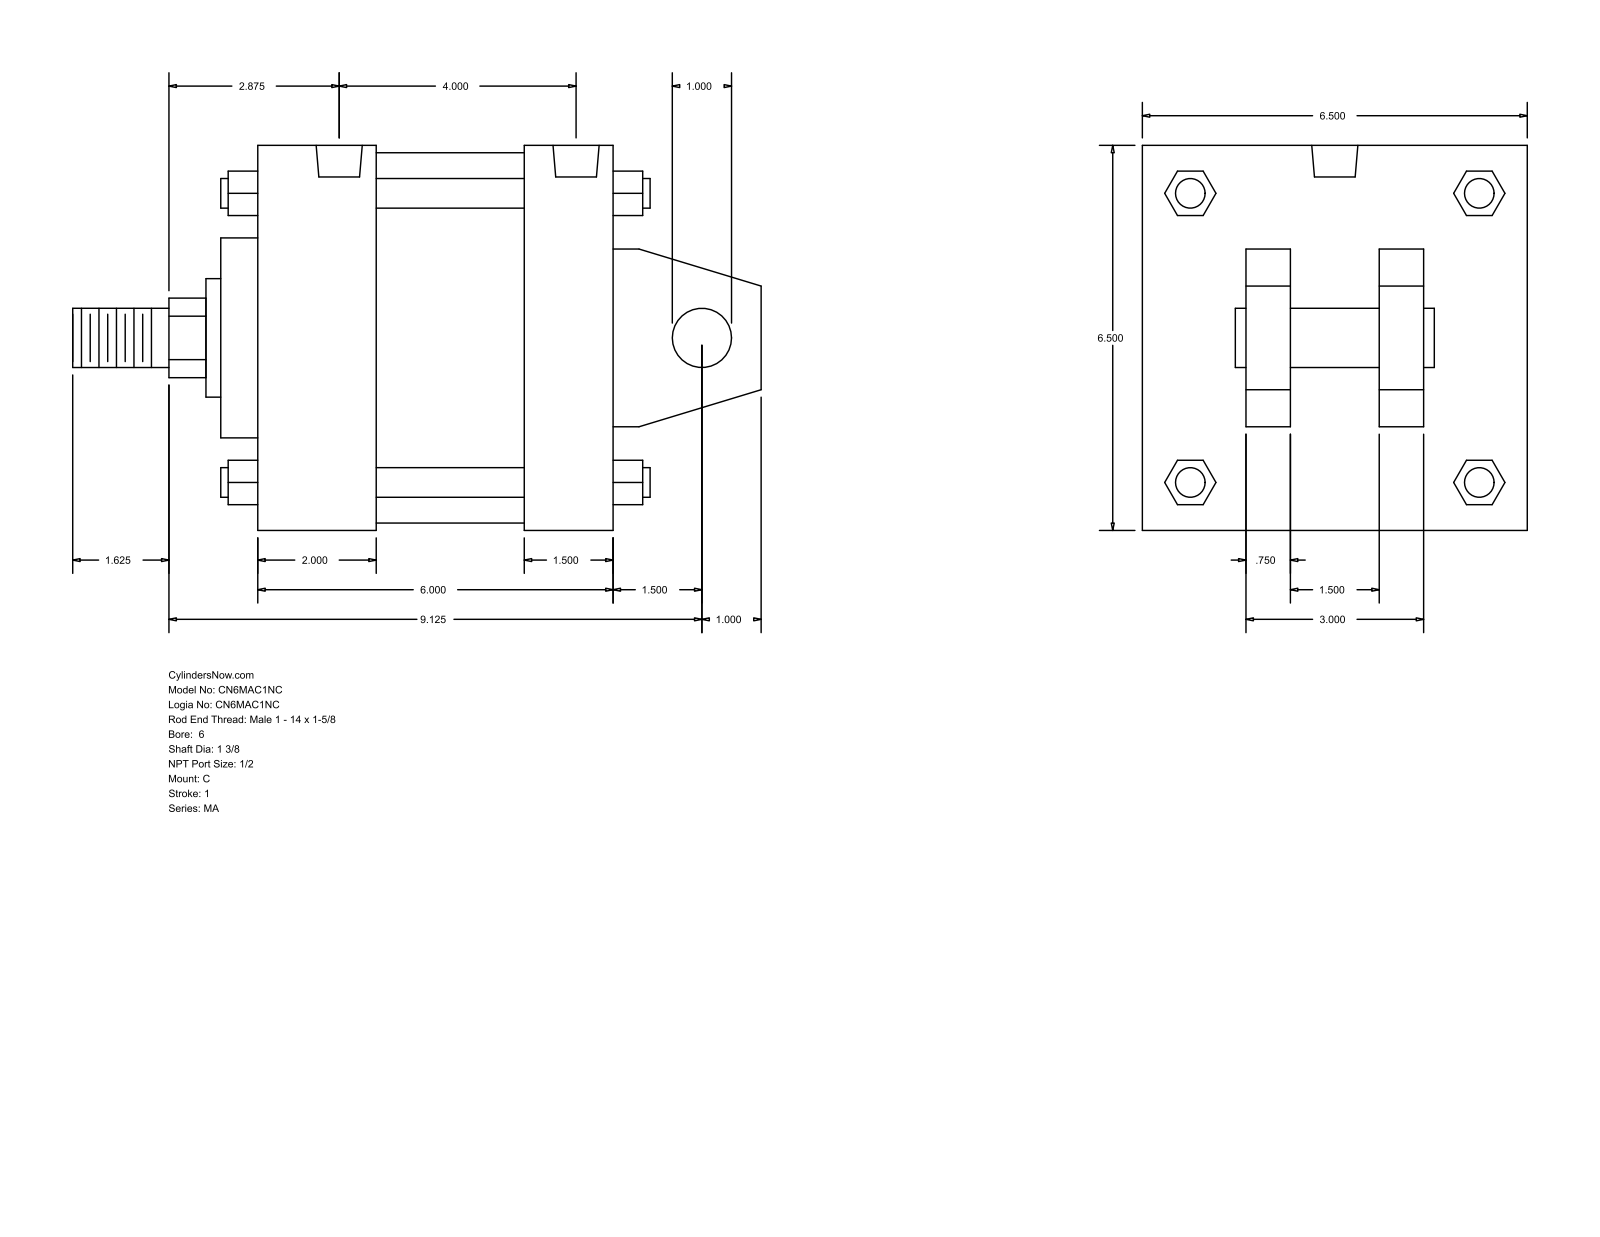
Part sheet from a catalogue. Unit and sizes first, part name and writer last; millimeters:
Units: millimetres
Overall size (bounding box): 295.27 × 165.1 × 165.1
Round holes (diameter × count): ⌀17.46 ×4, ⌀19.77 ×2
Round bosses / shafts (diameter × count): ⌀12.7 ×4, ⌀25.4 ×2, ⌀158.75 ×1, ⌀85.72 ×1, ⌀50.8 ×1, ⌀34.92 ×1
Partial cylindrical surfaces — rounded edges, fillets, slot ends (radius × count): R17.06 ×1
Main face-to-face distances: 165.1, 152.4, 63.5, 101.6, 38.1, 19.05, 50.8, 44.45, 120.65, 114.3
Hole centre spacings: 101.6, 3.17, 3.18, 98.42, 101.59, 104.77
Bodies: 0 solids, 141 faces (109 planar, 32 cylindrical, 0 other)
Part name (STEP PRODUCT): MA_C__0600_1.375
STEP written by: GSSL Pune (CONFIG_CONTROL_DESIGN)
